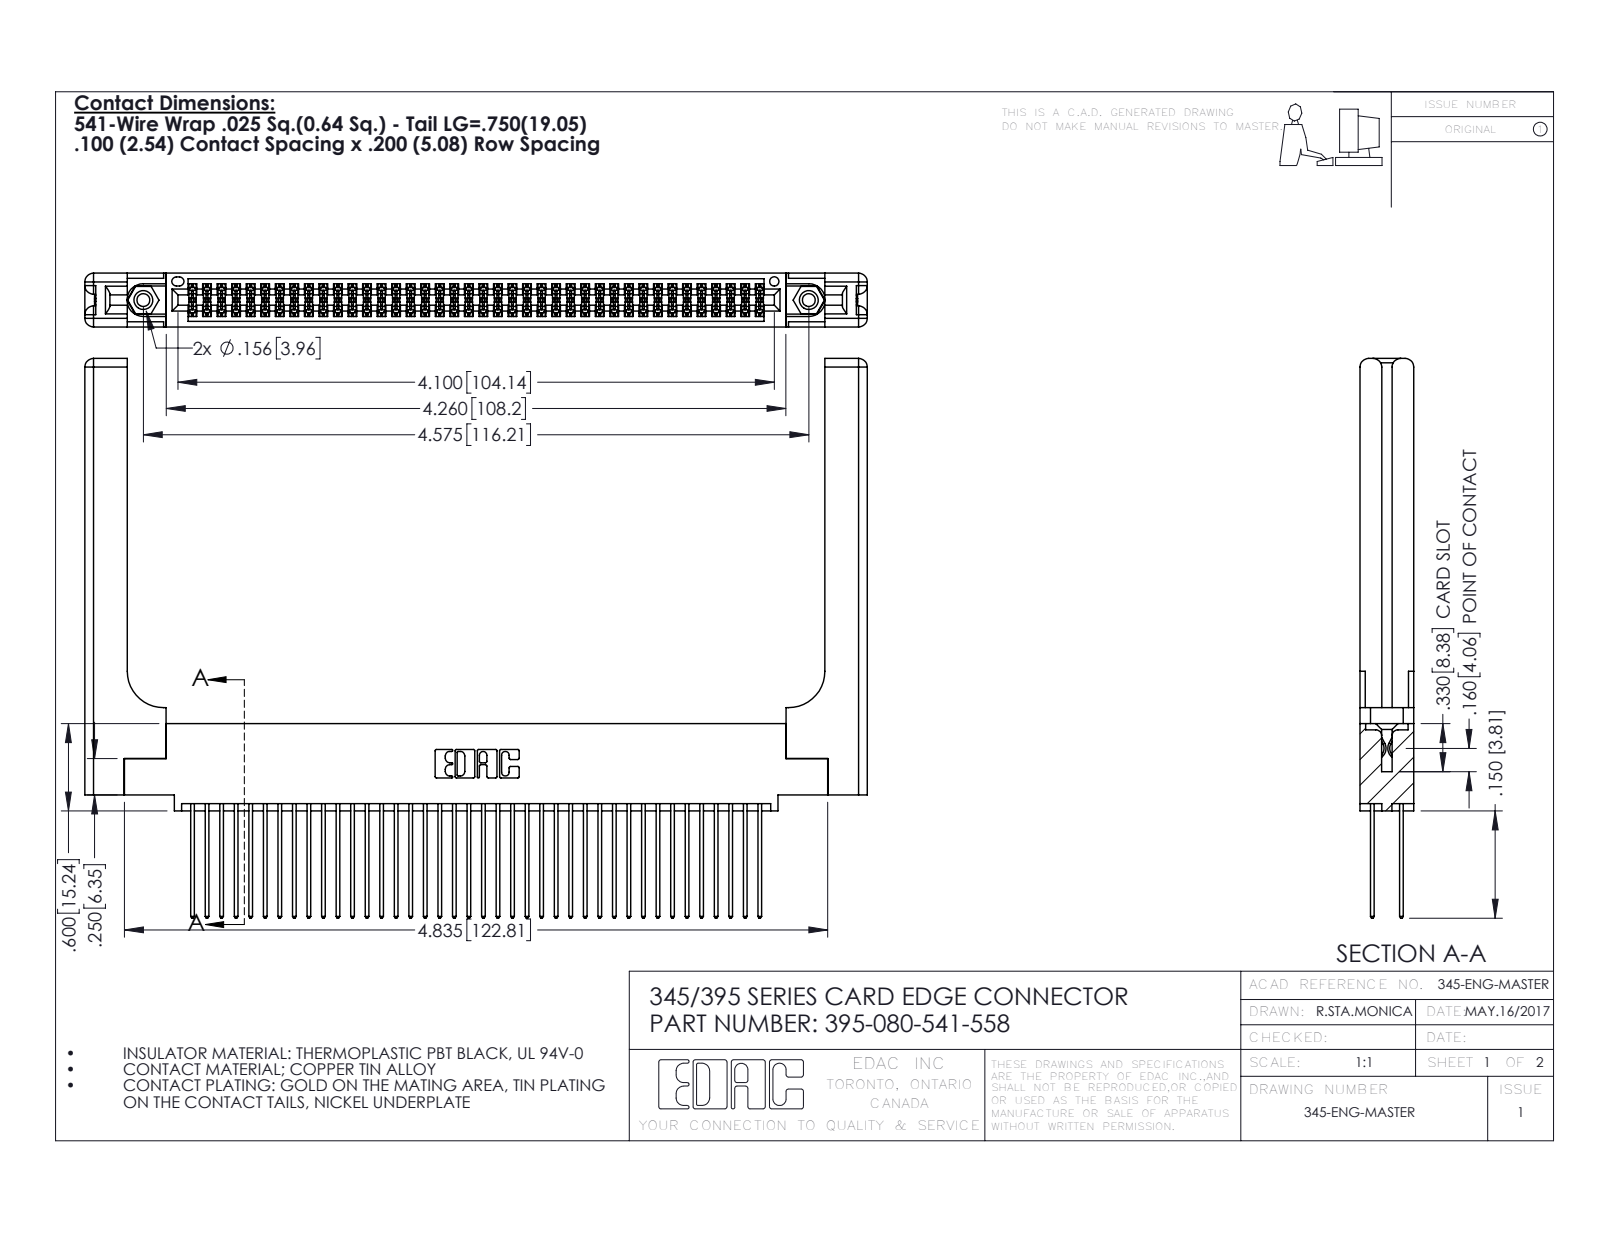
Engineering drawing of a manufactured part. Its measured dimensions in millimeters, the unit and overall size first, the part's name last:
Units: millimetres
Overall size (bounding box): 136.6 × 97.7 × 9.4
Round holes (diameter × count): ⌀2.3 ×2, ⌀3.2 ×2, ⌀4 ×2, ⌀1.6 ×1
Round bosses / shafts (diameter × count): ⌀3.9 ×2
Partial cylindrical surfaces — rounded edges, fillets, slot ends (radius × count): R0.2 ×120, R0.3 ×80, R0.3 ×22, R1.5 ×16, R0.2 ×6, R0.8 ×6, R0.7 ×3, R0.4 ×2
Main face-to-face distances: 1.8, 7.6, 9.4, 2.5, 6.9, 0.6, 5.1, 5.7, 4.4, 3.8
Hole centre spacings: 6.9, 110.2, 116.2
Volume: 22 110 mm³ · Surface area: 27 430 mm²
Bodies: 85 solids, 4386 faces (2872 planar, 1454 cylindrical, 60 other)
Part name (STEP PRODUCT): 345-220-058_345-220-058; 395-080-541-558; 345-250-001_345-250-001-102; 345-292-001_345-293-141 (+1 more)
STEP written by: SolidWorks 2016 (CONFIG_CONTROL_DESIGN)
